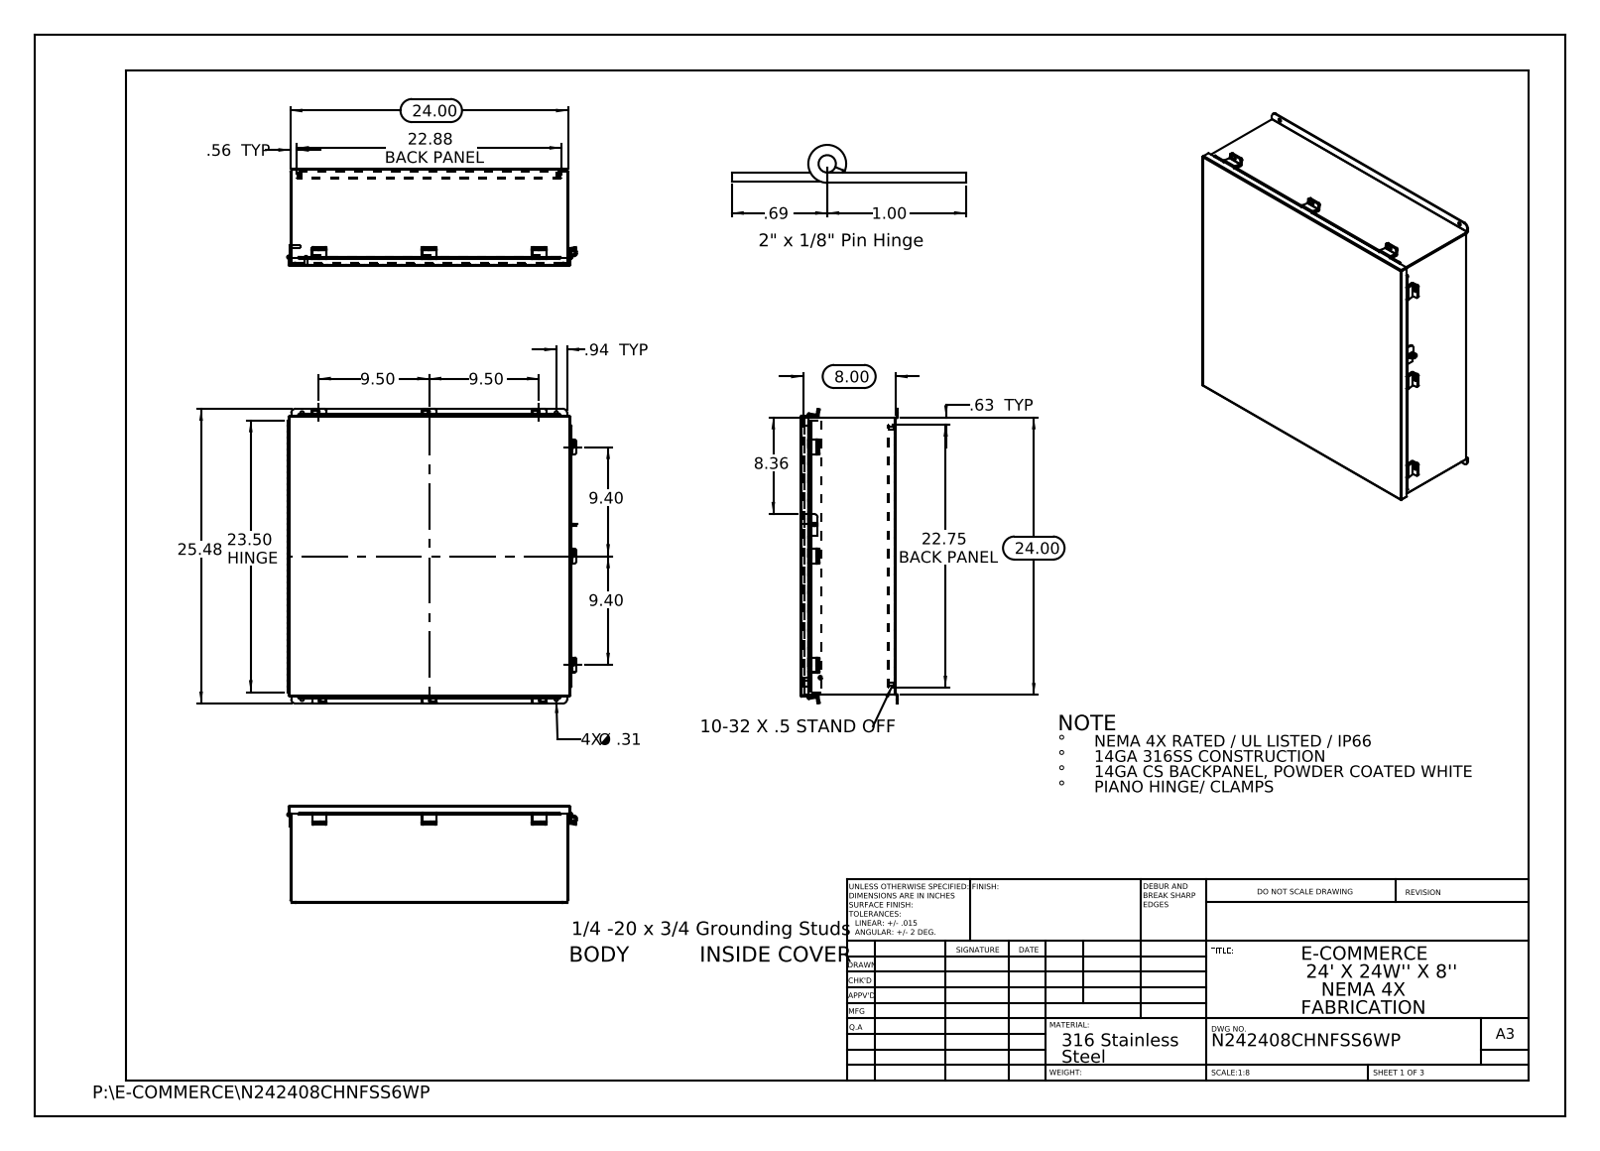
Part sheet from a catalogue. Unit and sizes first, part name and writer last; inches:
Units: inches
Overall size (bounding box): 25.476 × 25.072 × 8.39
Round holes (diameter × count): ⌀0.25 ×13, ⌀0.187 ×4, ⌀0.312 ×4, ⌀0.125 ×1, ⌀0.125 ×1, ⌀0.373 ×1, ⌀0.375 ×1
Round bosses / shafts (diameter × count): ⌀0.313 ×4, ⌀0.315 ×2, ⌀0.236 ×2, ⌀0.273 ×1, ⌀0.25 ×1
Partial cylindrical surfaces — rounded edges, fillets, slot ends (radius × count): R0.125 ×31, R0.133 ×18, R0.013 ×13, R0.009 ×12, R0.088 ×12, R0.083 ×6, R0.1 ×6, R0.375 ×4
Main face-to-face distances: 0.075, 8.128, 23.925, 8.053, 8.203, 7.628, 0.575, 0.5, 7.553, 0.649
Hole centre spacings: 1.315, 9.5, 22.213, 23.427, 32.257, 9.425, 19, 21.976
Volume: 198.7 in³ · Surface area: 5 373 in²
Bodies: 33 solids, 1148 faces (715 planar, 413 cylindrical, 20 other)
Part name (STEP PRODUCT): N242408CHNFSS6WP JIC Bottom; N242408CHNFSS6WP JIC Enclosure Template; N242408CHNFSS6WP JIC_Cover_Template; N242408CHNFSS6WP Hinge Body Side (+8 more)
STEP written by: SolidWorks 2013 (CONFIG_CONTROL_DESIGN)
